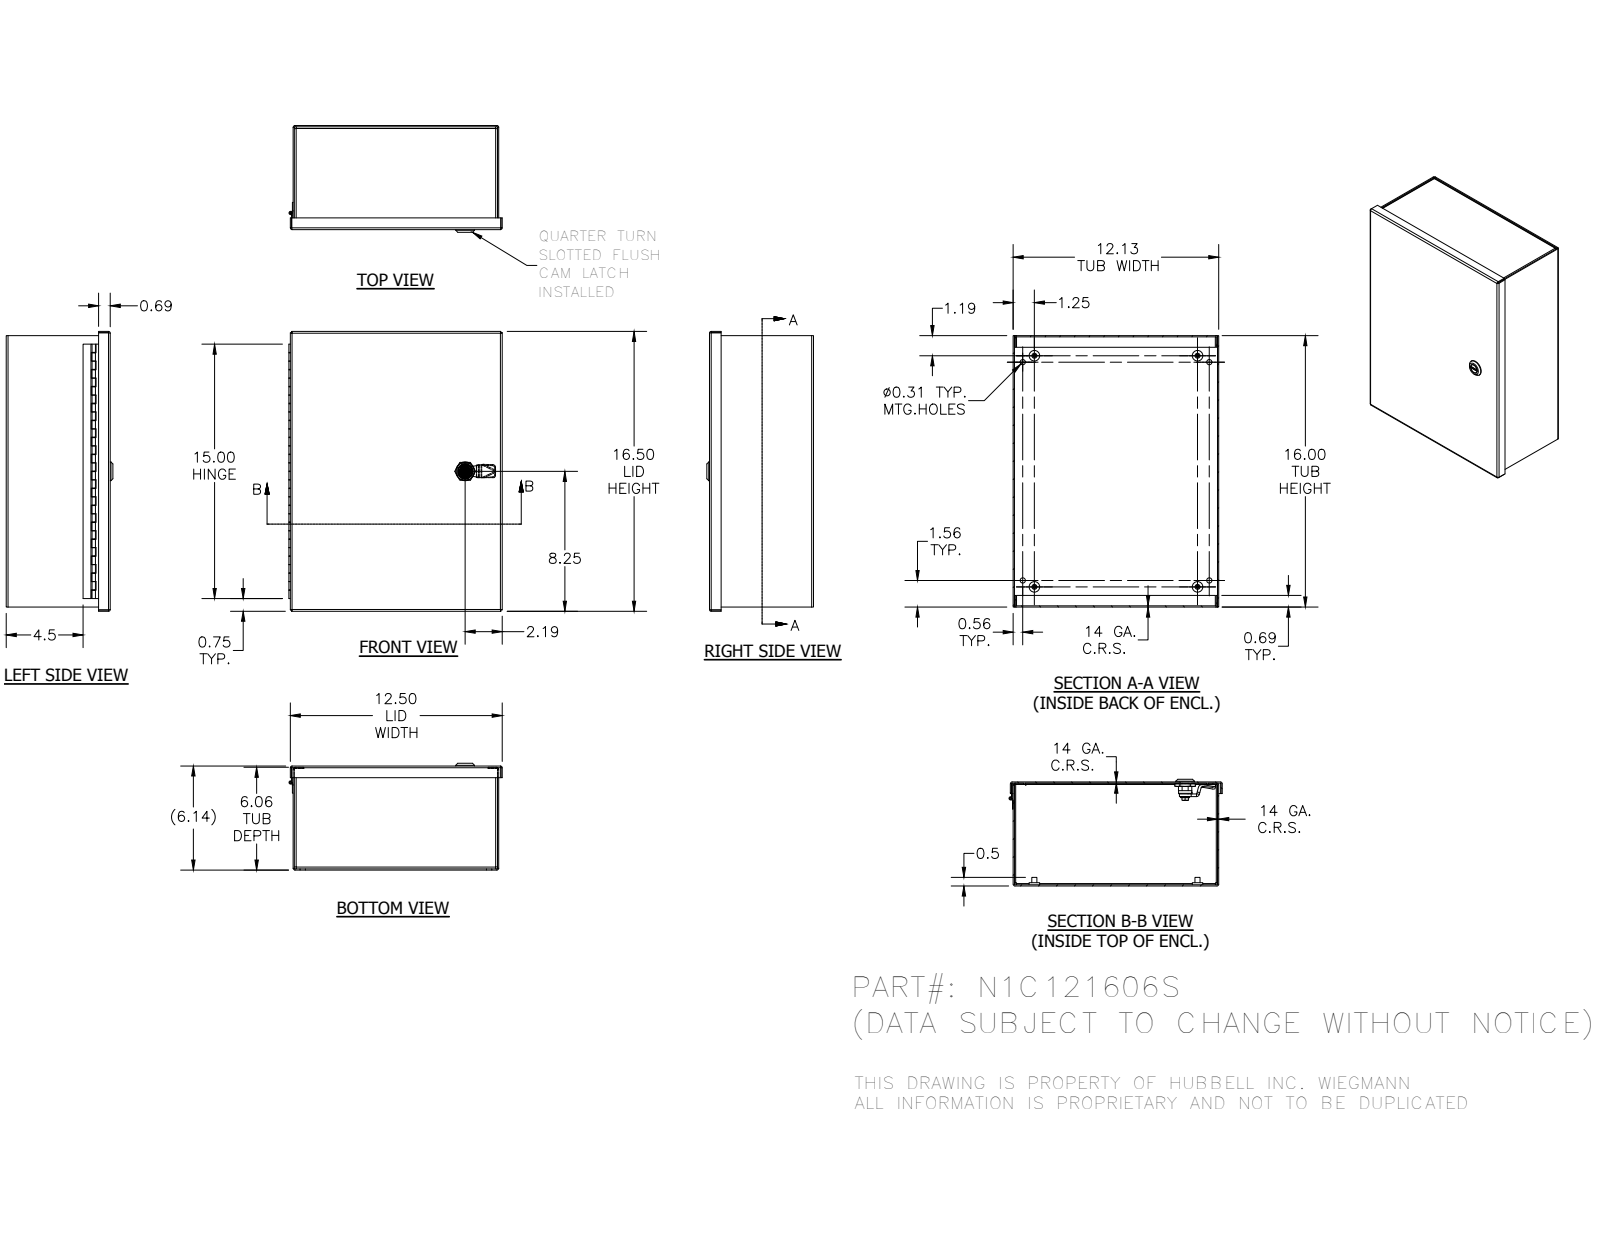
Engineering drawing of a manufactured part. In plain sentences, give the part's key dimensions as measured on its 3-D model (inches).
The part is named "N1C121606S; N1C1206STB; N1C121606SBLR; HFW3513 (+8 more)". Its 3-D file was written by "Autodesk Inventor 2012 (AUTOMOTIVE_DESIGN)". It is 19 solids with 755 faces: 435 planar, 238 cylindrical and 82 other. Overall it measures 16.5 by 12.584 by 6.294 inches. Its volume is 63.19 cubic inches and its surface area 1 747 square inches. Round holes: 4 of diameter 0.156, 4 of diameter 0.313, 1 of diameter 0.116, 1 of diameter 0.197, 1 of diameter 0.315, 1 of diameter 0.394, 1 of diameter 0.402, 1 of diameter 0.634, 1 of diameter 0.802. Round bosses or shafts: 4 of diameter 0.625, 4 of diameter 0.3, 1 of diameter 1.102, 1 of diameter 0.866, 1 of diameter 0.78, 1 of diameter 0.63, 1 of diameter 0.598, 1 of diameter 0.531. Partial cylindrical surfaces (rounded edges, fillets, slot ends): 30 of radius 0.012, 16 of radius 0.031, 16 of radius 0.105, 10 of radius 0.02, 4 of radius 0.157, 3 of radius 0.016, 1 of radius 0.039, 1 of radius 0.173. The main face-to-face distances are 0.074, 6.063, 5.989, 12.051, 6.137, 15.926, 11.977, 12.125, 16, 15.852. The hole center spacings are 0.783, 10.319, 13.268, 16.79, 6.592, 6.852, 9.625, 11.
